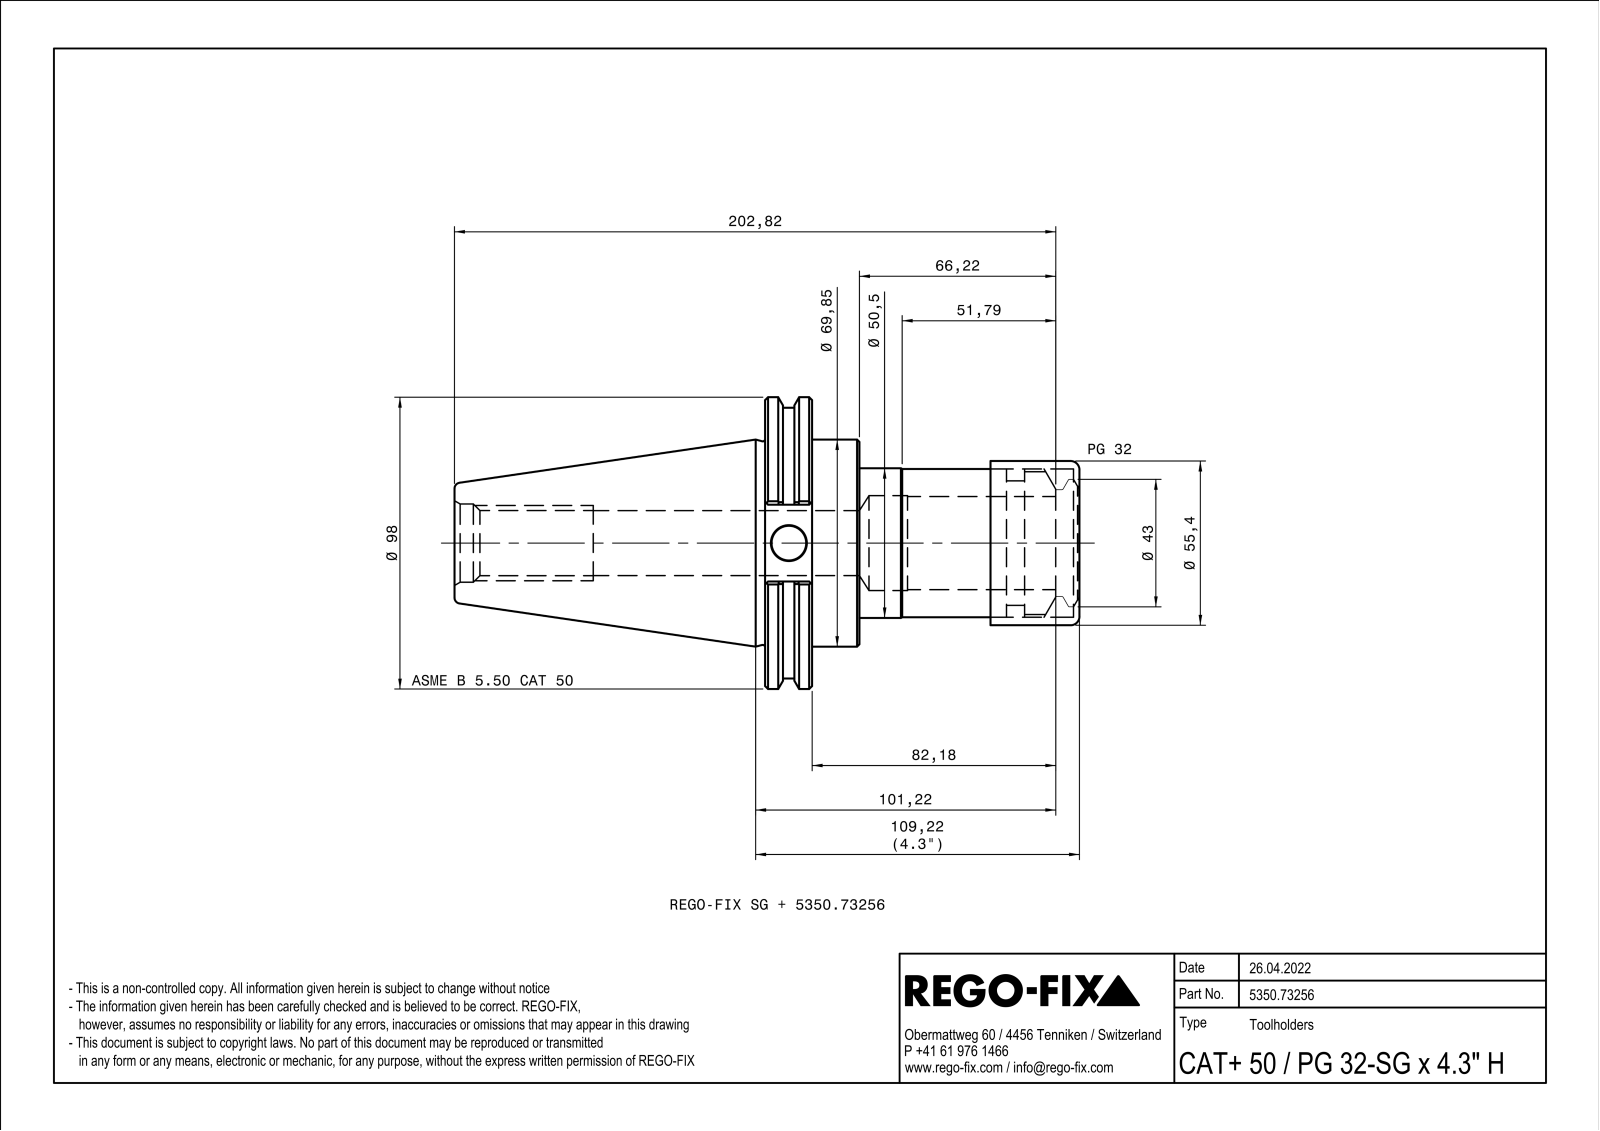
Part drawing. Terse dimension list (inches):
name: NOCUT
written by: SIEMENS PLM Software Solid Edge ST10 (AUTOMOTIVE_DESIGN)
unit: in
bodies: 1 solid, 124 faces (55 planar, 25 cylindrical, 44 other)
size: 8.3 × 3.875 × 3.718
volume: 28.26 in³; area: 117.3 in²
holes: 1× ⌀0.472, 1× ⌀0.865, 1× ⌀1.039, 1× ⌀1.299, 1× ⌀1.506, 1× ⌀1.905, 1× ⌀1.97, 1× ⌀2.008
bosses: 1× ⌀3.875, 1× ⌀3.594, 1× ⌀2.75, 1× ⌀2.726, 1× ⌀2.181, 1× ⌀2.165, 1× ⌀1.988, 1× ⌀1.969
rounds: 4× R0.02
face distances: 0.691, 0.63, 1.321, 2.92, 3.55, 4.241, 8.3, 5.38, 4.75, 4.059
